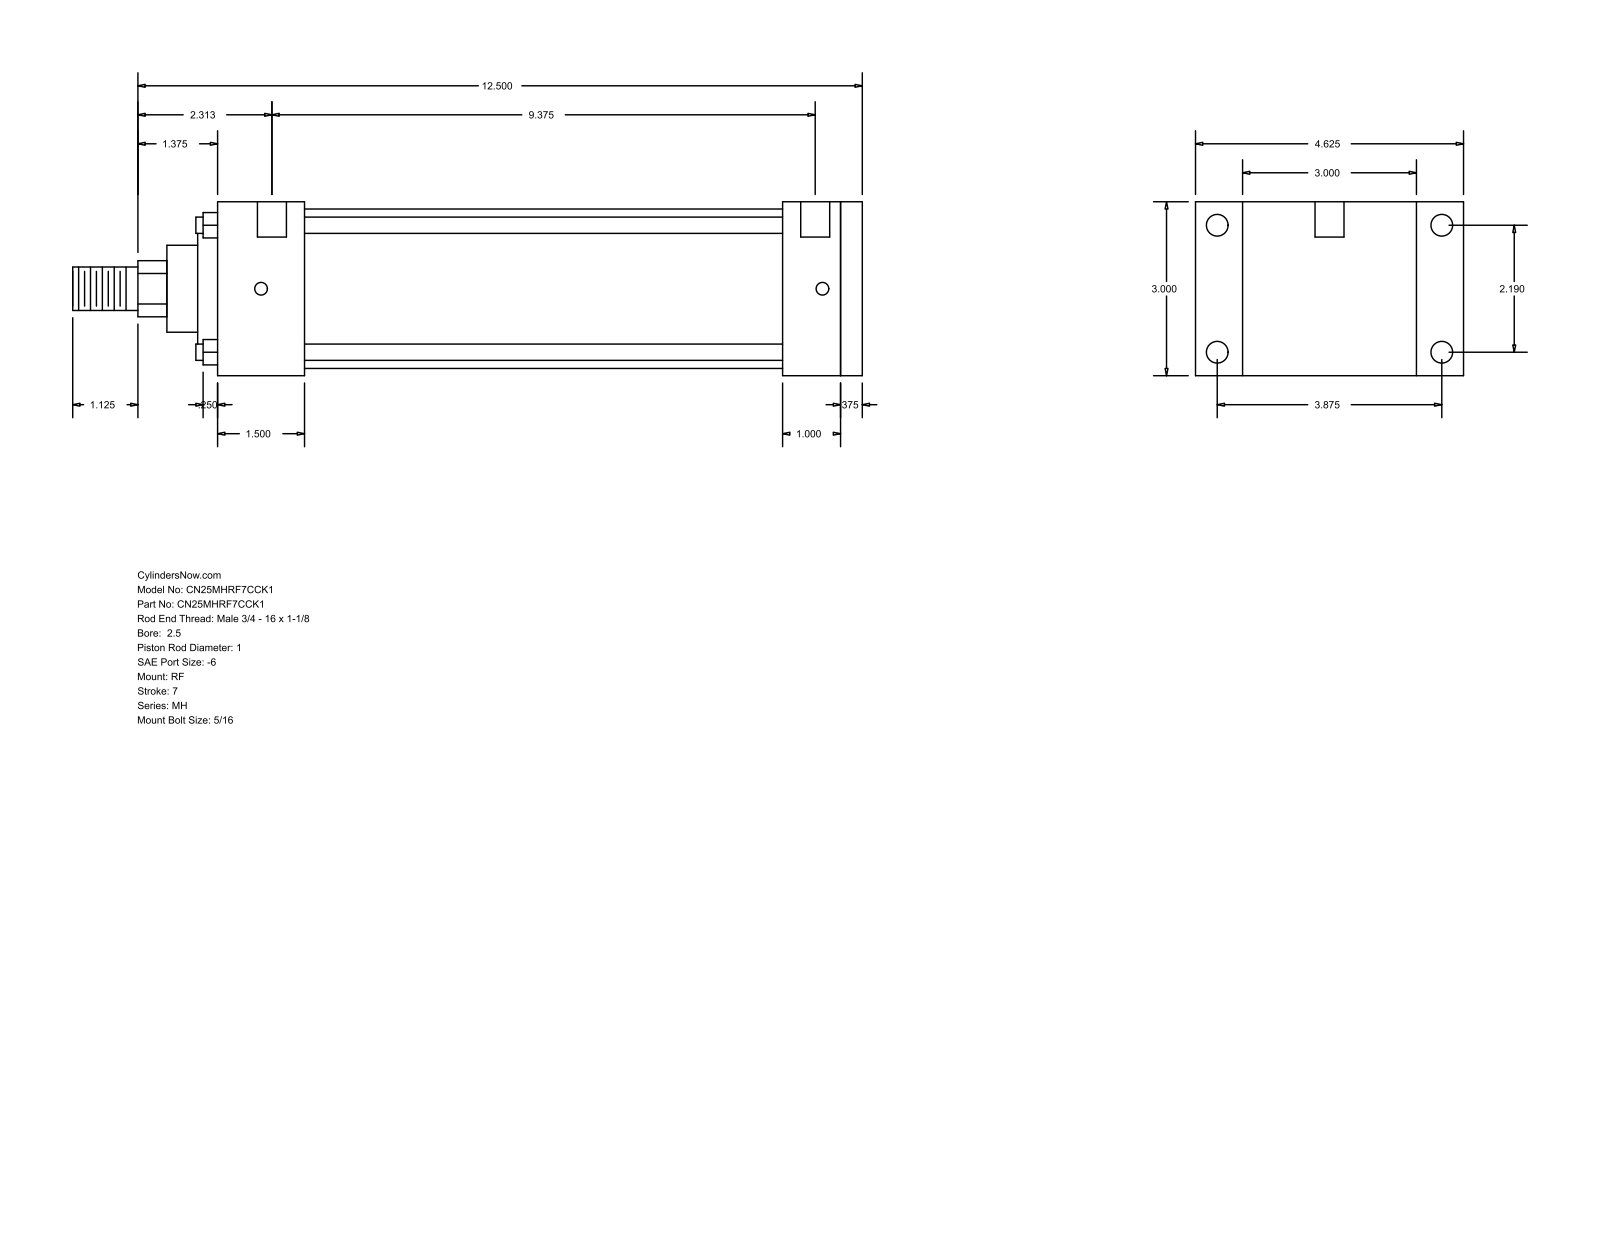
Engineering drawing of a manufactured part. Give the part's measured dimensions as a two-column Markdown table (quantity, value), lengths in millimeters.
| quantity | value |
| --- | --- |
| part name | MH_RF__0250_1 |
| STEP written by | GSSL Pune (CONFIG_CONTROL_DESIGN) |
| units | millimeters |
| bodies | 0 solids, 94 faces (65 planar, 29 cylindrical, 0 other) |
| overall size | 346.07 × 117.47 × 76.2 |
| round holes (diameter × count) | 5.56 × 4, 9.53 × 4, 12.7 × 2 |
| round bosses / shafts (diameter × count) | 7.14 × 4, 69.85 × 1, 60.33 × 1, 38.1 × 1, 25.4 × 1, 19.05 × 1 |
| partial cylindrical surfaces (radius × count) | 12.29 × 1 |
| main face-to-face distances | 76.2, 9.52, 282.58, 273.06, 247.65, 25.41, 34.93, 38.11, 209.54, 234.95 |
| hole center spacings | 55.62, 98.42, 113.05, 246.06, 3.18, 4.76, 238.12, 241.3 |
